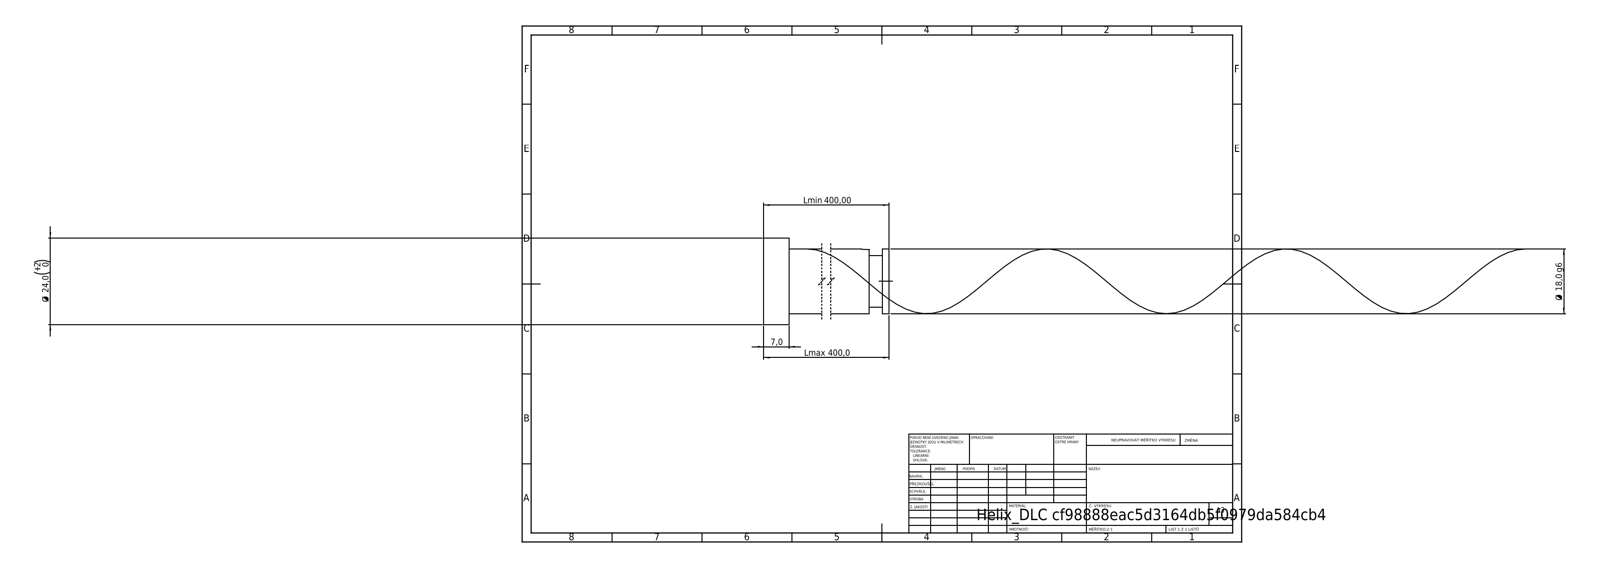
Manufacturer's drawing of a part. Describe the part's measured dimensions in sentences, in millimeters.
Its 3-D file was written by "SolidWorks 2019 (CONFIG_CONTROL_DESIGN)". It is 1 solid with 21 faces: 6 planar, 14 cylindrical and 1 other. Overall it measures 400 by 24 by 24 millimeters. Its volume is 101 869 cubic millimeters and its surface area 24 296 square millimeters. Round bosses or shafts: 1 of diameter 24, 1 of diameter 18, 1 of diameter 14.4. The main face-to-face distances are 400, 7, 393, 398.1, 391.1, 1.9, 394.5, 387.5, 3.6, 5.5.
